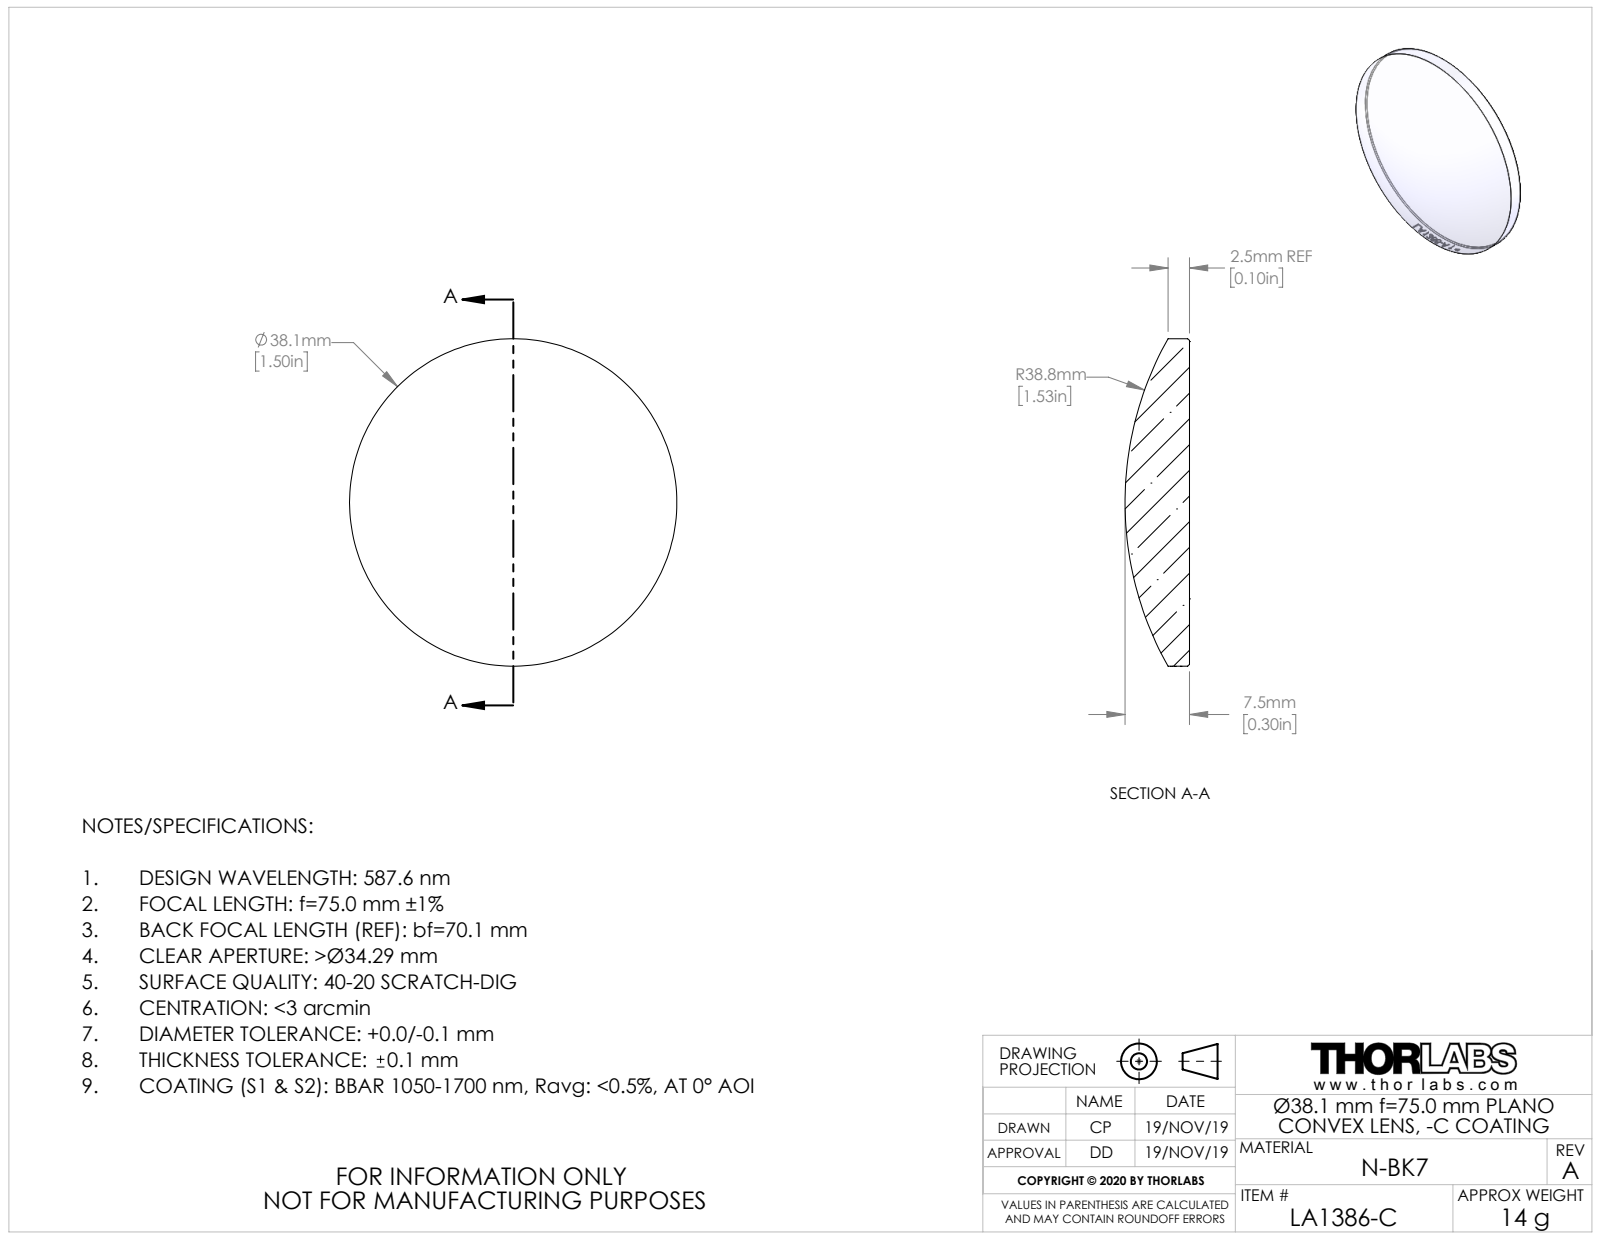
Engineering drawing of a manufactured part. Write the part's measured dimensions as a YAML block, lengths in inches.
part_name: "TTN200739-E0W"
step_written_by: "SolidWorks 2018 (CONFIG_CONTROL_DESIGN)"
units: inches
bodies: {solids: 1, faces: 24, planar: 1, cylindrical: 19, other: 4}
overall_size: [1.5, 1.5, 0.295]
volume: 0.352
surface_area: 4.098
round_bosses_or_shafts:
  - {diameter: 1.5, count: 1}
